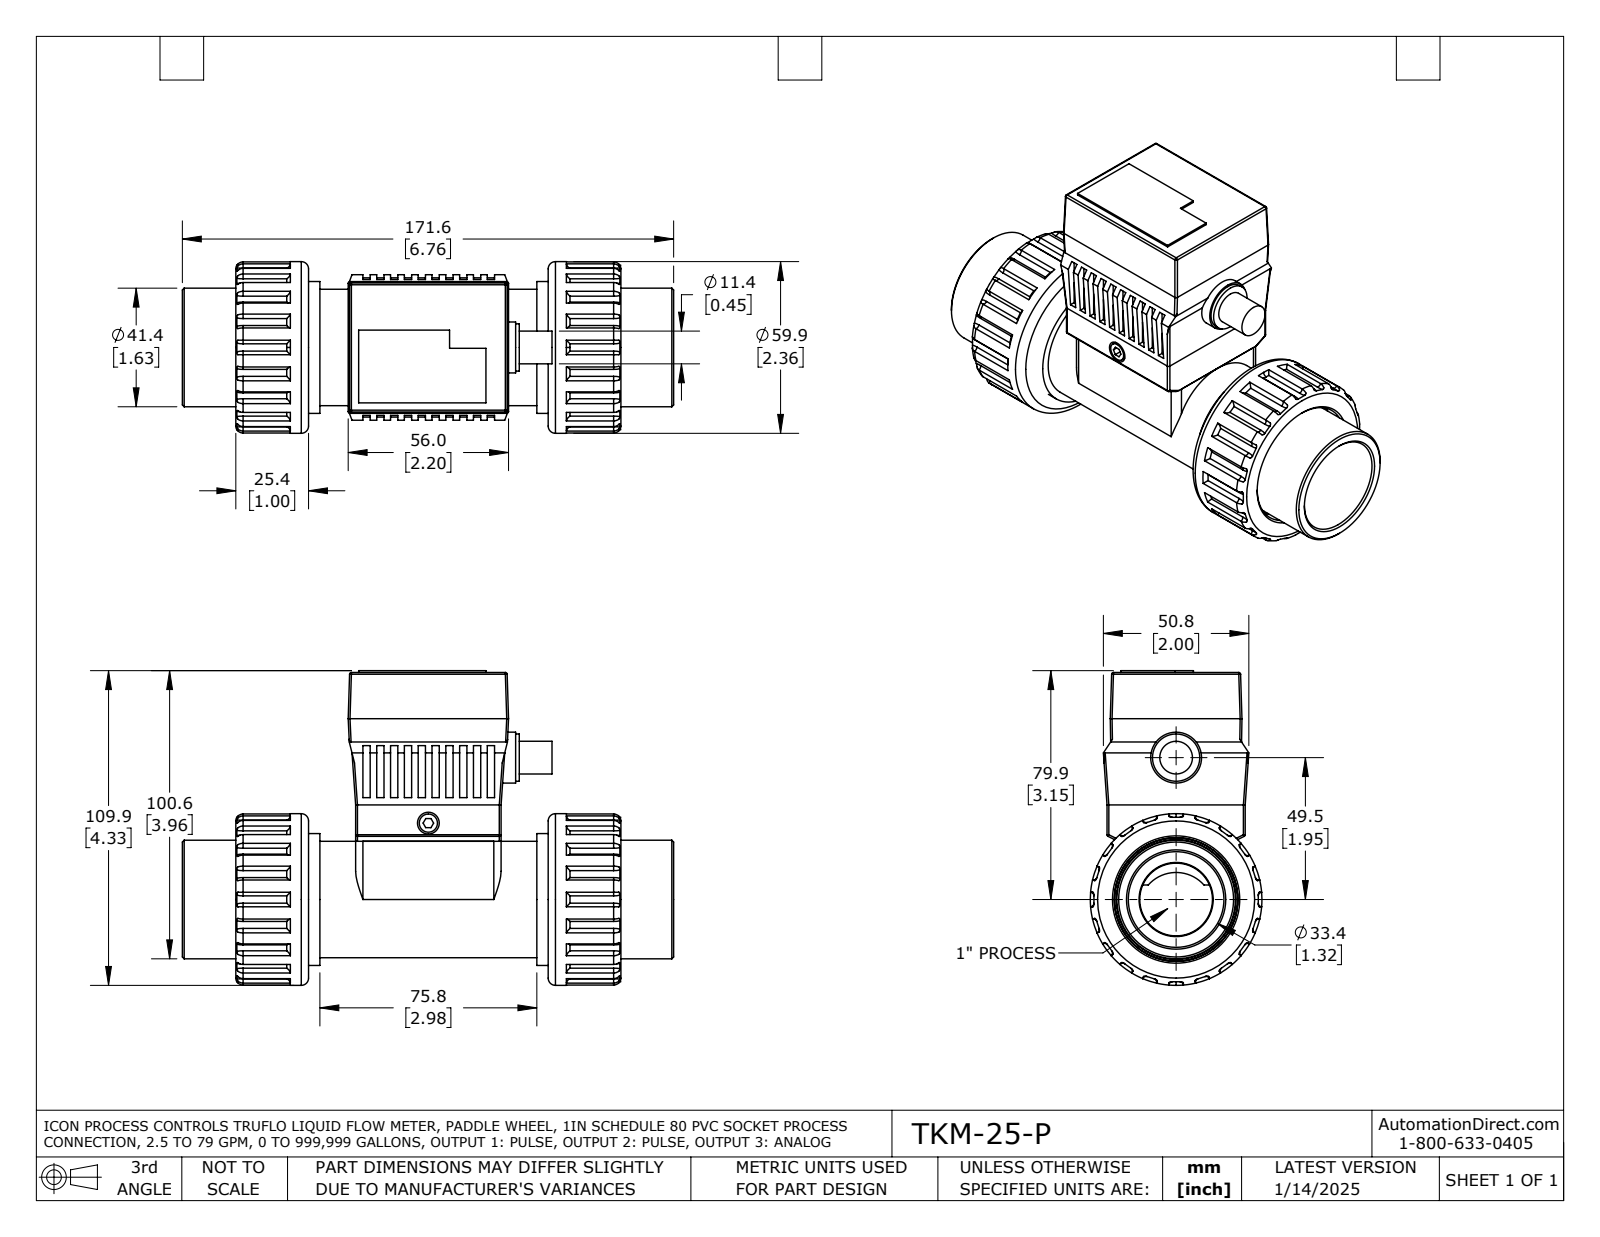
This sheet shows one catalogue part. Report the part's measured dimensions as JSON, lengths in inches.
{"part_name": "TKM-25-P", "step_written_by": "SolidWorks 2021 (AUTOMOTIVE_DESIGN)", "units": "inches", "bodies": {"solids": 7, "faces": 634, "planar": 240, "cylindrical": 190, "other": 204}, "overall_size": [6.755, 4.325, 2.36], "volume_in3": 21.44, "surface_area_in2": 142.8, "round_holes": [[0.128, 4], [0.3, 1], [1, 1], [1.02, 1], [1.1, 1], [1.2, 1], [1.315, 1], [1.5, 1], [1.695, 1], [1.7, 1]], "round_bosses_or_shafts": [[2.36, 1], [1.813, 1], [1.75, 1], [1.63, 1], [1.6, 1], [1.25, 1], [1.024, 1], [0.7, 1]], "partial_cylinders_radius": [[0.05, 40], [0.025, 26], [0.1, 4], [0.465, 1], [0.512, 1]], "face_to_face_distances": [3.815, 0.52, 1, 4.295, 0.48, 4.815, 1.648, 3.648, 1.167, 3.167], "hole_center_spacings": [0.979, 1.181, 1.561, 1.957]}
